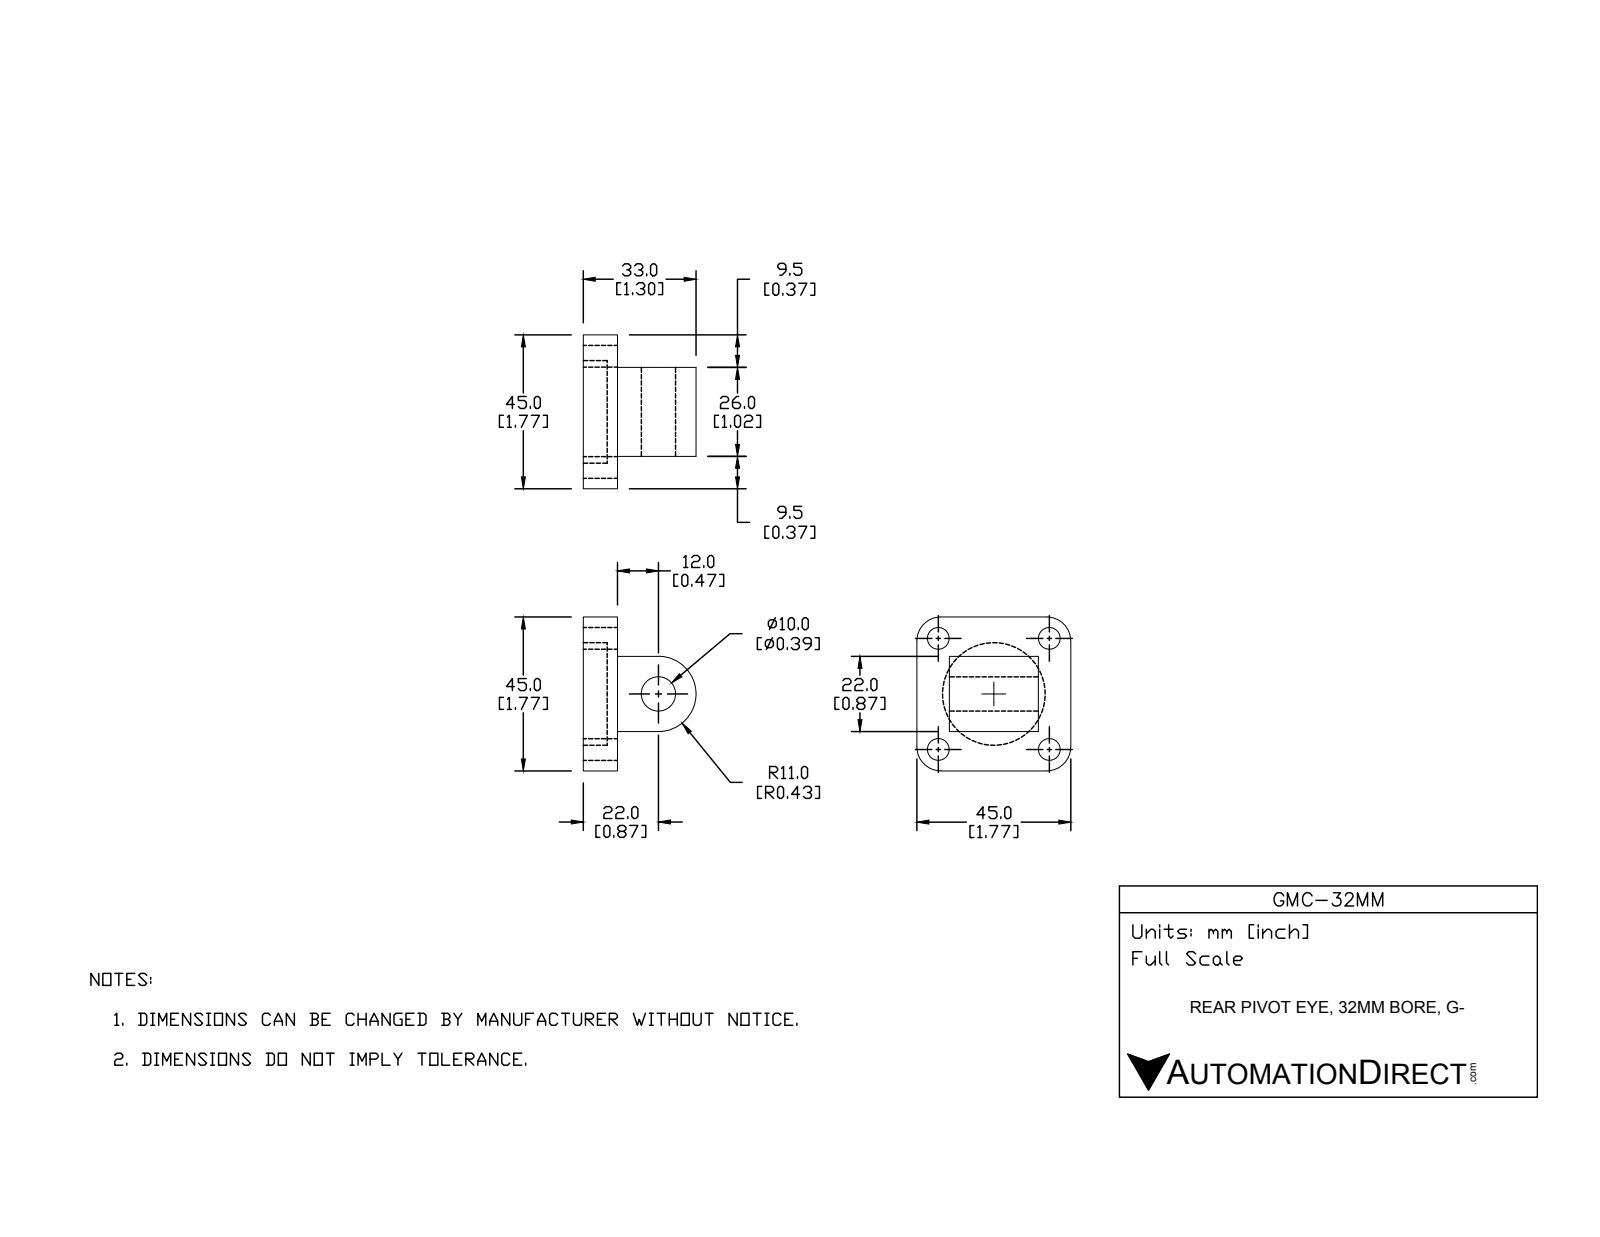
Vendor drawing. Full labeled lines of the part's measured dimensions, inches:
Part name (STEP PRODUCT): GMC-32MM
STEP written by: SolidWorks 2017 (AUTOMOTIVE_DESIGN)
Units: inches
Bodies: 1 solid, 28 faces (11 planar, 17 cylindrical, 0 other)
Overall size (bounding box): 1.772 × 1.772 × 1.299
Volume: 1.316 in³ · Surface area: 14.7 in²
Round holes (diameter × count): ⌀0.252 ×4, ⌀0.394 ×1, ⌀1.378 ×1
Partial cylindrical surfaces — rounded edges, fillets, slot ends (radius × count): R0.276 ×4, R0.433 ×1
Main face-to-face distances: 0.118, 0.276, 0.394, 0.374, 1.398, 0.453, 1.319, 1.772, 1.024, 0.866
Hole centre spacings: 0.905, 1.28, 1.809
